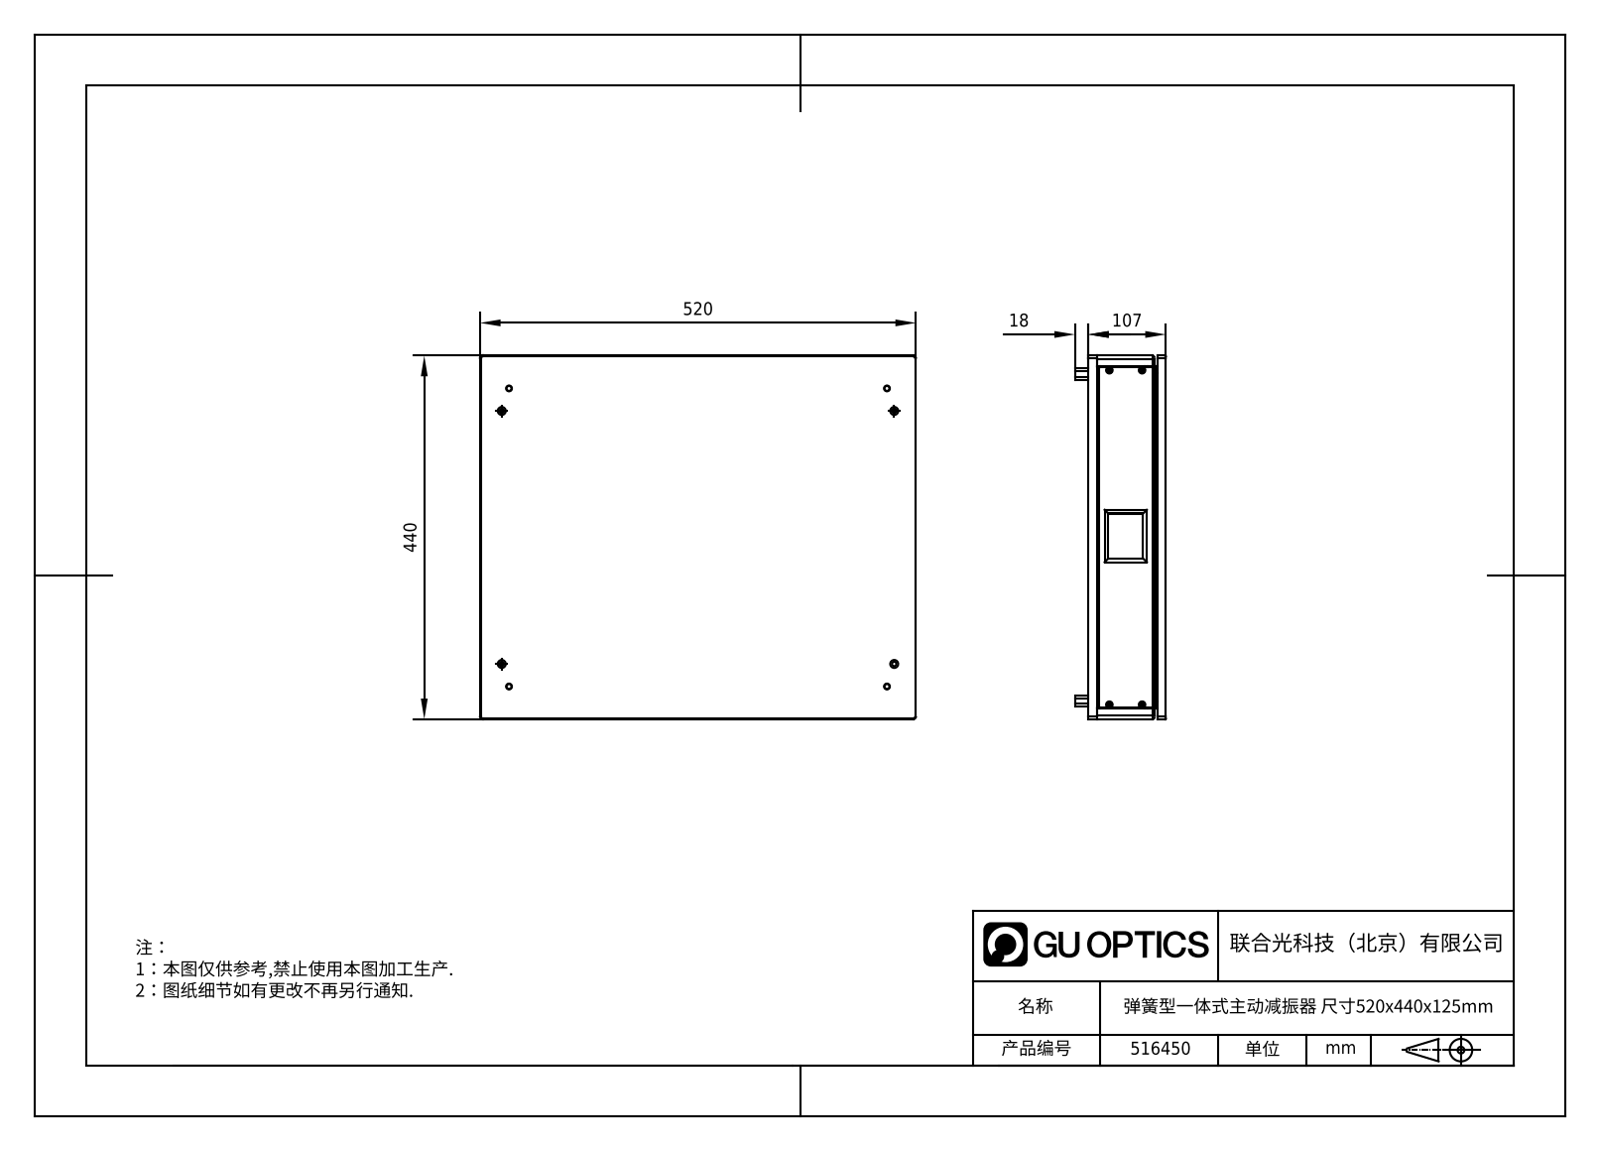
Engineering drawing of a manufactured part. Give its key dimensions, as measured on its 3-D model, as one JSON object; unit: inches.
{"part_name": "516450", "step_written_by": "SolidWorks 2020 (CONFIG_CONTROL_DESIGN)", "units": "inches", "bodies": {"solids": 37, "faces": 1409, "planar": 695, "cylindrical": 569, "other": 145}, "overall_size": [20.472, 17.323, 4.921], "volume_in3": 525.4, "surface_area_in2": 3461, "round_holes": [[0.315, 52], [0.13, 50], [0.177, 38], [0.169, 32], [0.205, 26], [0.098, 24], [0.165, 18], [0.354, 18], [0.394, 16], [0.217, 8], [0.268, 8], [0.201, 4]], "round_bosses_or_shafts": [[0.039, 9], [0.296, 8], [0.157, 8], [0.315, 4]], "partial_cylinders_radius": [[0.079, 26], [0.039, 20], [0.197, 18], [0.118, 12], [0.02, 8], [0.029, 8], [0.108, 8], [0.315, 8]], "face_to_face_distances": [0.472, 3.74, 3.228, 0.512, 0.039, 3.268, 3.701, 4.213, 0.984, 2.756], "hole_center_spacings": [0.501, 1.772, 16.185, 19.334, 25.209, 1.939, 2.378, 3.102]}
